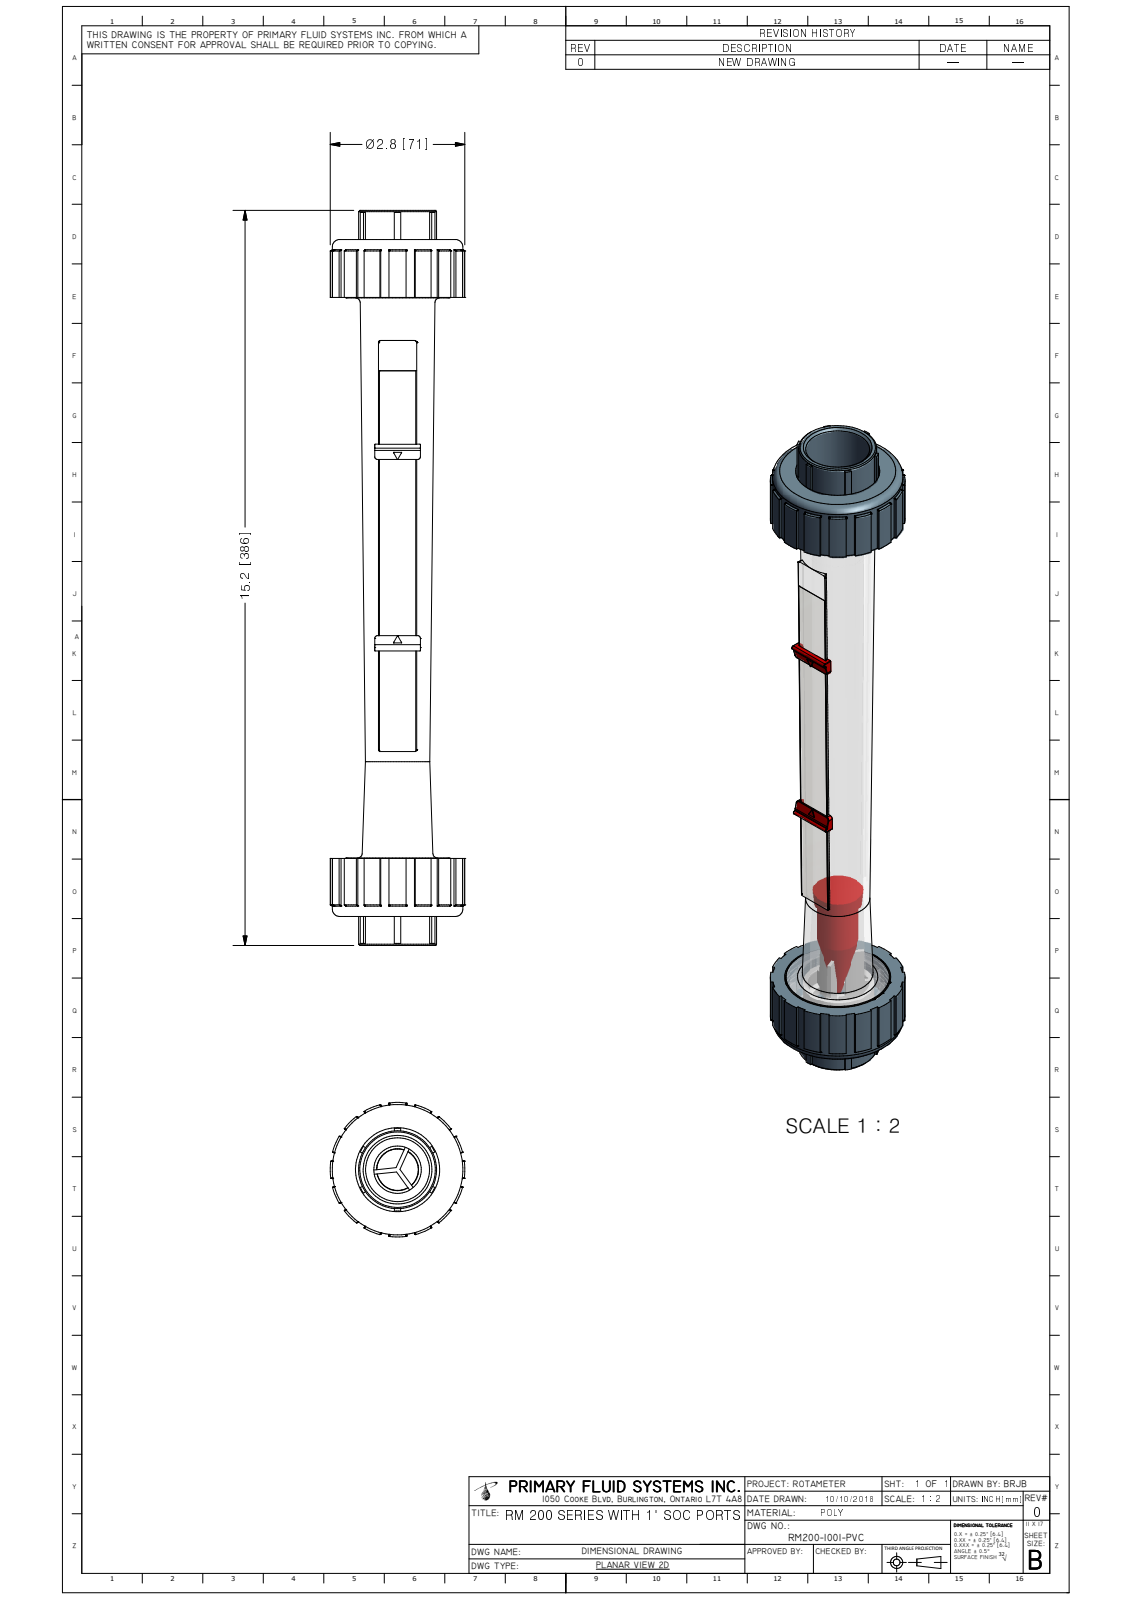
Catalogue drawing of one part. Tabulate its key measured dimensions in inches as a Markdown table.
| quantity | value |
| --- | --- |
| part name | RM200-100I-PVC_R0 |
| STEP written by | Autodesk Inventor 2009 (AUTOMOTIVE_DESIGN) |
| units | inches |
| bodies | 1 solid, 571 faces (234 planar, 138 cylindrical, 199 other) |
| overall size | 15.2 × 2.783 × 2.783 |
| volume | 31.79 in³ |
| surface area | 173 in² |
| round holes (diameter × count) | 1.32 × 1, 1.738 × 1, 2.19 × 1 |
| round bosses / shafts (diameter × count) | 2.697 × 1, 2.152 × 1, 2.022 × 1, 1.61 × 1, 1.485 × 1 |
| partial cylindrical surfaces (radius × count) | 0.008 × 18, 0.01 × 16, 0.004 × 10, 0.006 × 4, 0.06 × 4, 0.008 × 2, 0.04 × 2, 0.045 × 2 |
| main face-to-face distances | 1.197, 12.799, 0.367, 13.629, 0.83, 12.432, 1.207, 12.789, 11.592, 0.84 |
